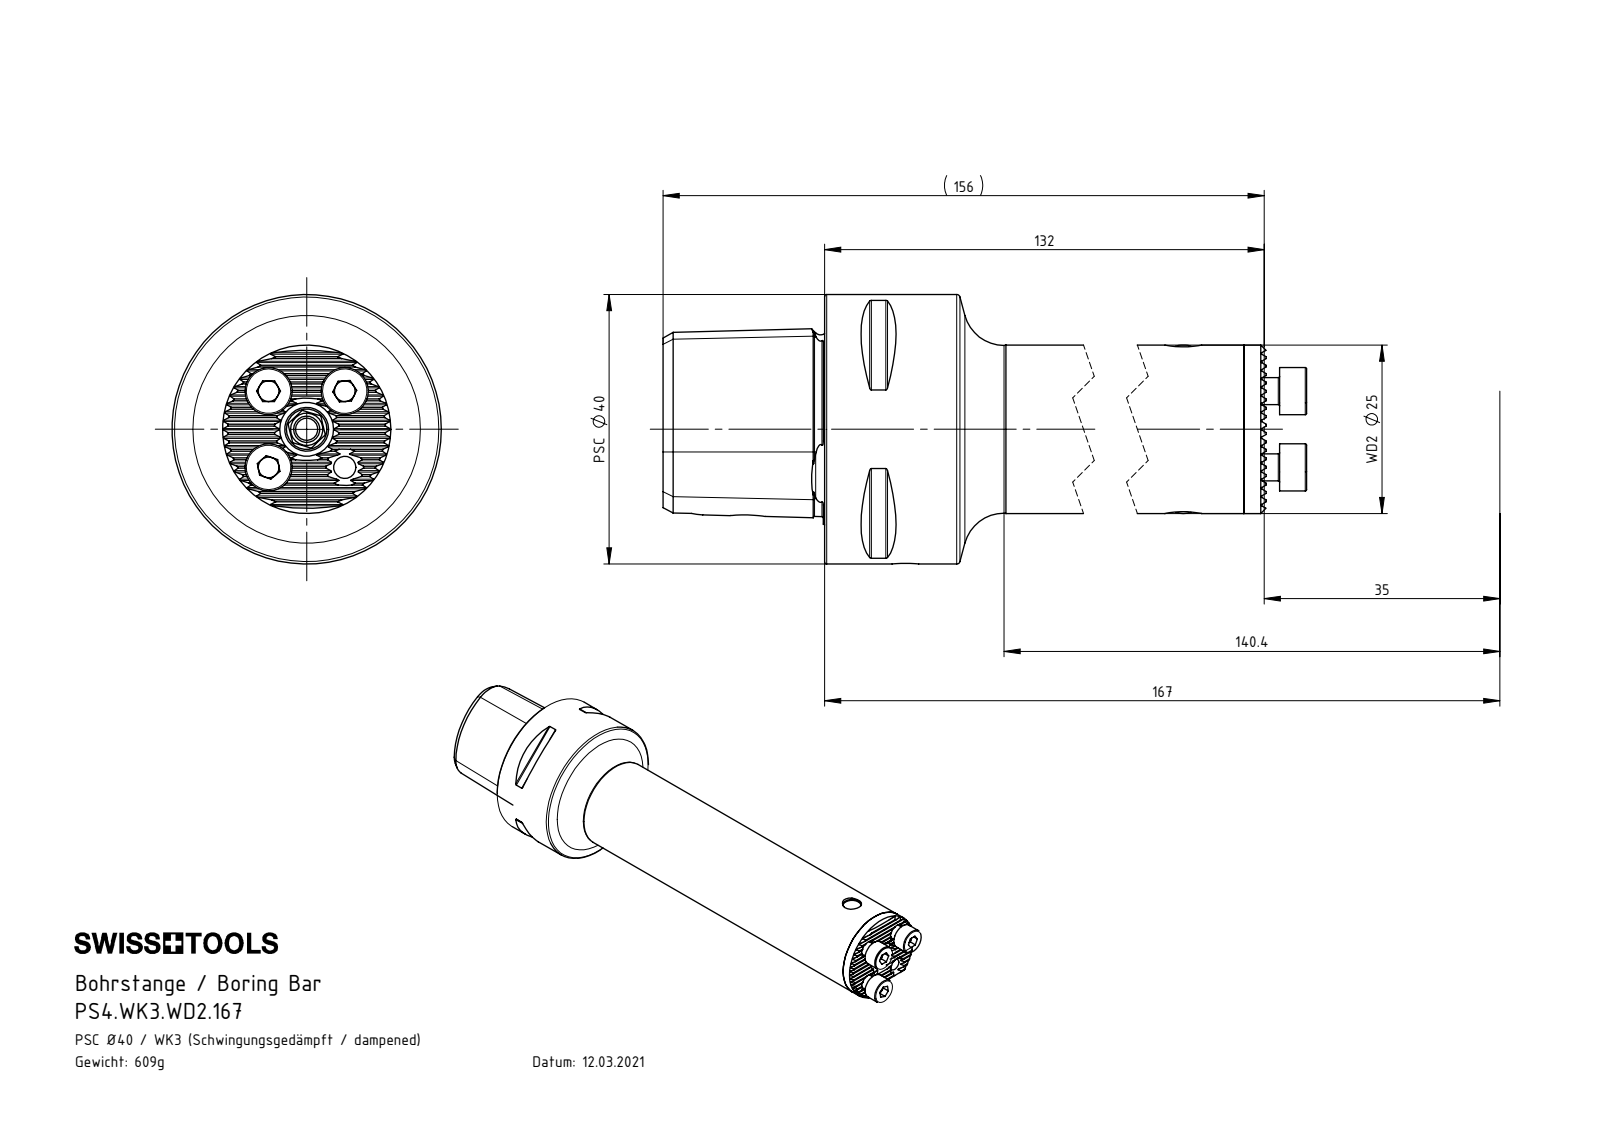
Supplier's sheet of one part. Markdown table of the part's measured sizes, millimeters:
| quantity | value |
| --- | --- |
| part name | WD2-ER1.021.019_A; WD2-ER1.008.037_A; DIN 3771 - 10x4; DIN 3771 - 6x1 (+8 more) |
| STEP written by | SolidWorks 2017 (AUTOMOTIVE_DESIGN) |
| units | millimeters |
| bodies | 16 solids, 497 faces (236 planar, 110 cylindrical, 151 other) |
| overall size | 162.3 × 40 × 40 |
| volume | 80 253 mm³ |
| surface area | 39 225 mm² |
| round holes (diameter × count) | 3.3 × 5, 4 × 1, 4.6 × 1, 5 × 1, 5.5 × 1, 6 × 1, 6.5 × 1, 6.8 × 1, 7.4 × 1, 9 × 1, 10.2 × 1, 11 × 1 |
| round bosses / shafts (diameter × count) | 7 × 3, 4 × 3, 40 × 1, 25 × 1, 21 × 1, 20.7 × 1, 17.8 × 1, 10 × 1 |
| partial cylindrical surfaces (radius × count) | 0.12 × 19, 0.3 × 8, 3 × 1 |
| main face-to-face distances | 6, 48.4, 3.2, 4.33, 113, 1.08, 9.2, 45.2, 39.2, 6.75 |
| hole center spacings | 8, 11.32, 16.01, 23.5, 108, 131.5 |
